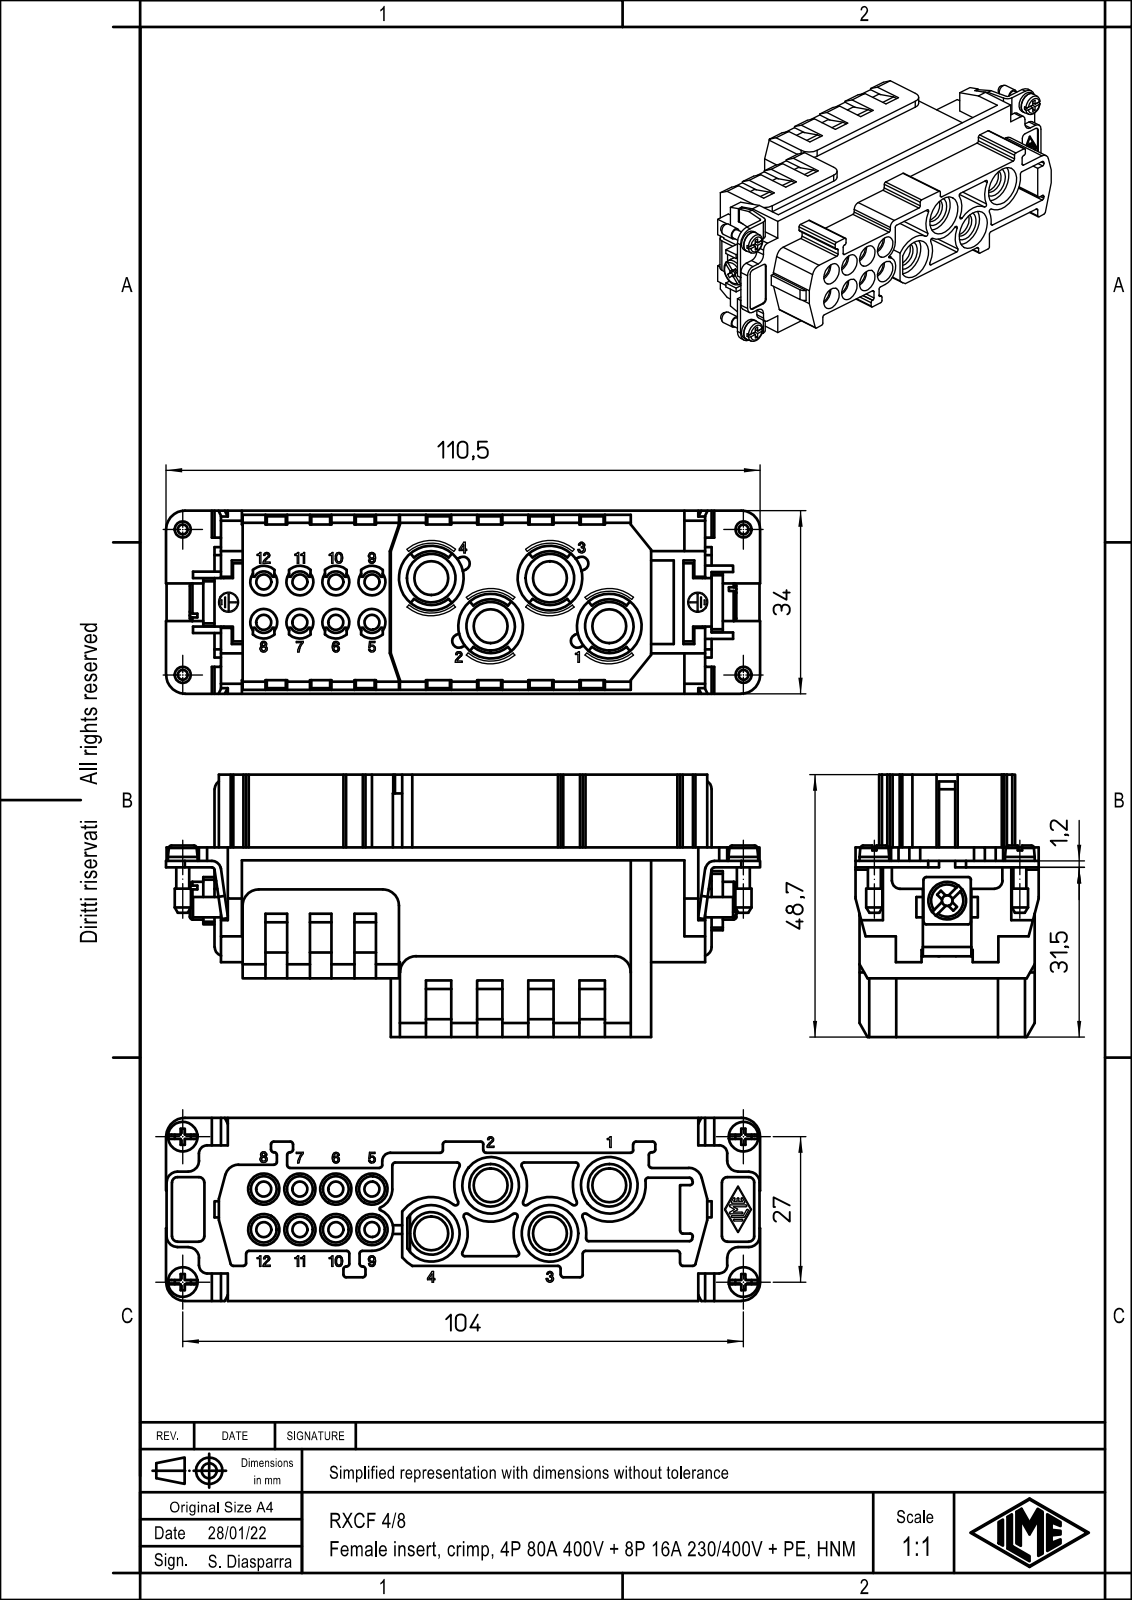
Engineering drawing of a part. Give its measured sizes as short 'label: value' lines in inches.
name: RXCF_4-8
written by: Creo Elements/Direct Modeling 20.1B 02-Apr-2019 (C) Parametric Technology GmbH (AUTOMOTIVE_DESIGN)
unit: in
bodies: 1 solid, 1705 faces (1358 planar, 295 cylindrical, 52 other)
size: 4.339 × 1.917 × 1.339
volume: 4.551 in³; area: 57.34 in²
holes: 8× ⌀0.11, 8× ⌀0.197, 8× ⌀0.228, 4× ⌀0.248, 4× ⌀0.354, 4× ⌀0.472, 3× ⌀0.413, 1× ⌀0.079
bosses: 4× ⌀0.217, 4× ⌀0.118, 4× ⌀0.094, 1× ⌀0.276
rounds: 66× R0.02, 15× R0.007, 12× R0.118, 8× R0.039, 8× R0.077, 8× R0.079, 7× R0.059, 6× R0.067
face distances: 0.071, 1.209, 0.226, 0.982, 0.872, 0.337, 0.266, 0.943, 0.717, 1.138
hole spacings: 0.264, 0.396, 0.295, 0.528, 0.605, 0.557, 0.791, 0.844
